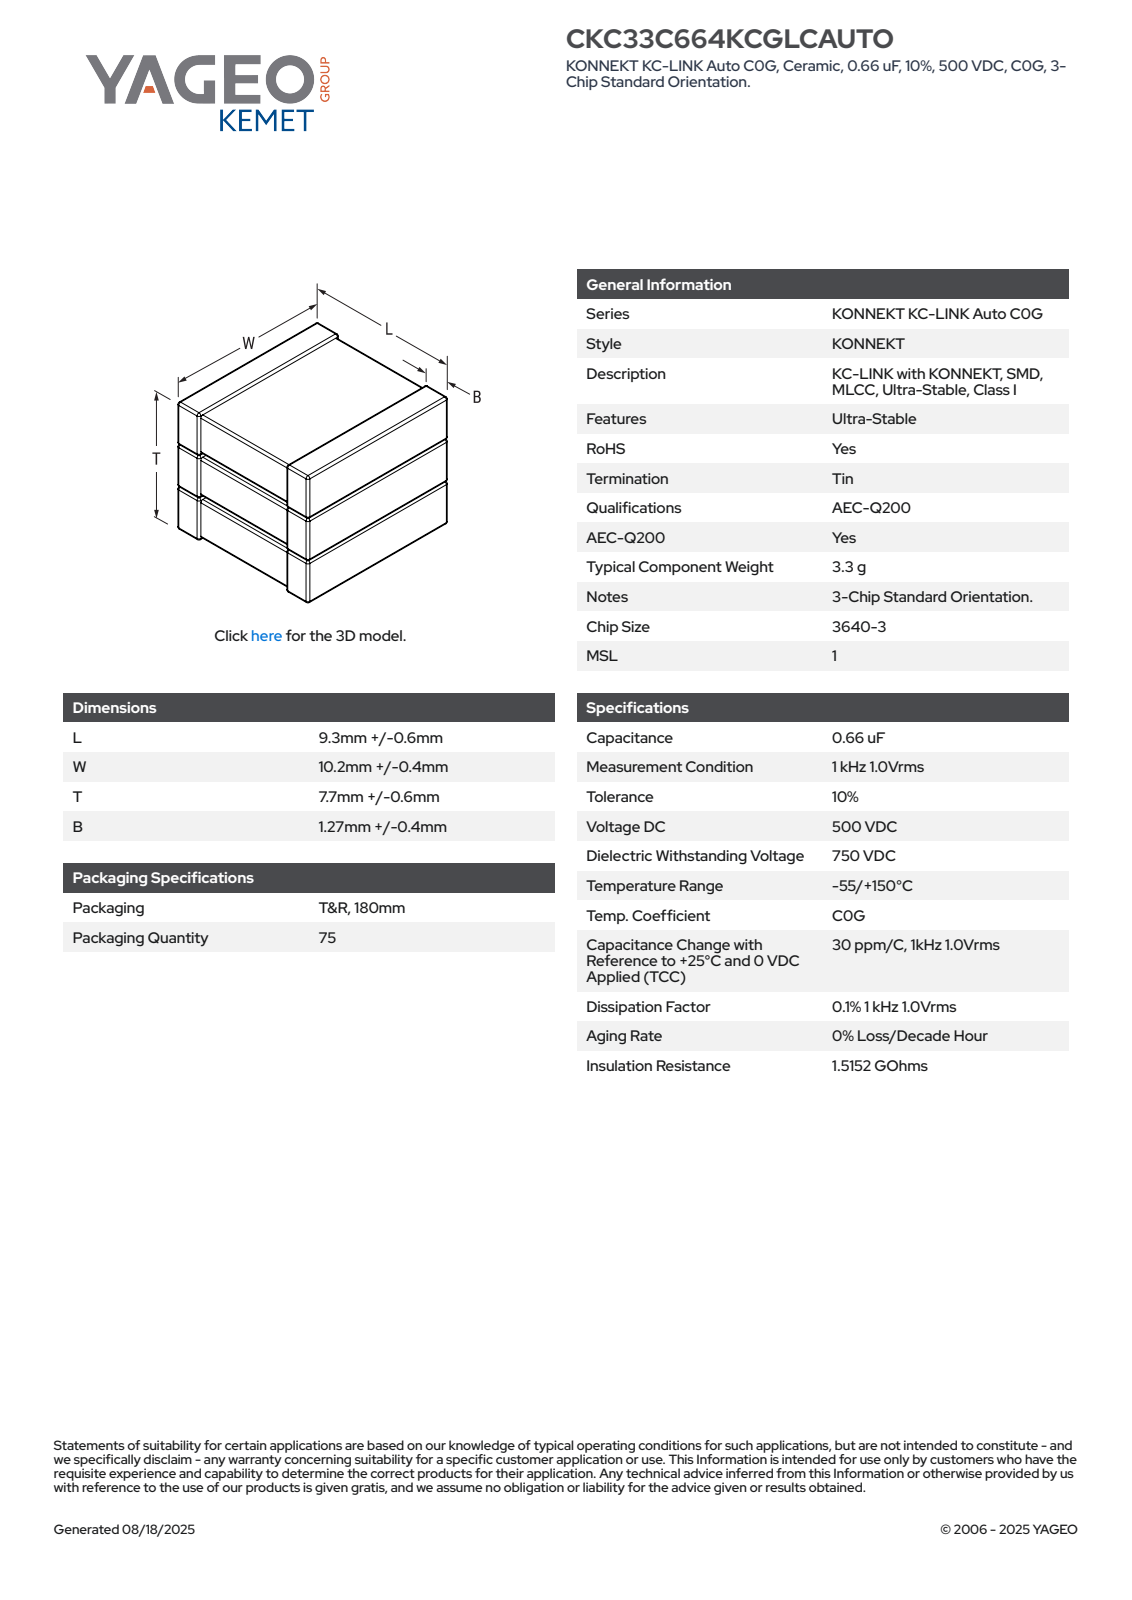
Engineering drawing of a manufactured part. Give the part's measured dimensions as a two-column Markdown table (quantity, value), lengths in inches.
| quantity | value |
| --- | --- |
| part name | CCSS_K3T_3640_L9.9W10.6B1.67T8.3 |
| STEP written by | SolidWorks 2021 (AUTOMOTIVE_DESIGN) |
| units | inches |
| bodies | 6 solids, 249 faces (99 planar, 102 cylindrical, 48 other) |
| overall size | 0.417 × 0.39 × 0.327 |
| volume | 0.049 in³ |
| surface area | 1.47 in² |
| partial cylindrical surfaces (radius × count) | 0.006 × 56 |
| main face-to-face distances | 0.109, 0.098, 0.103, 0.115, 0.212, 0.207, 0.218, 0.104, 0.39, 0.316 |
